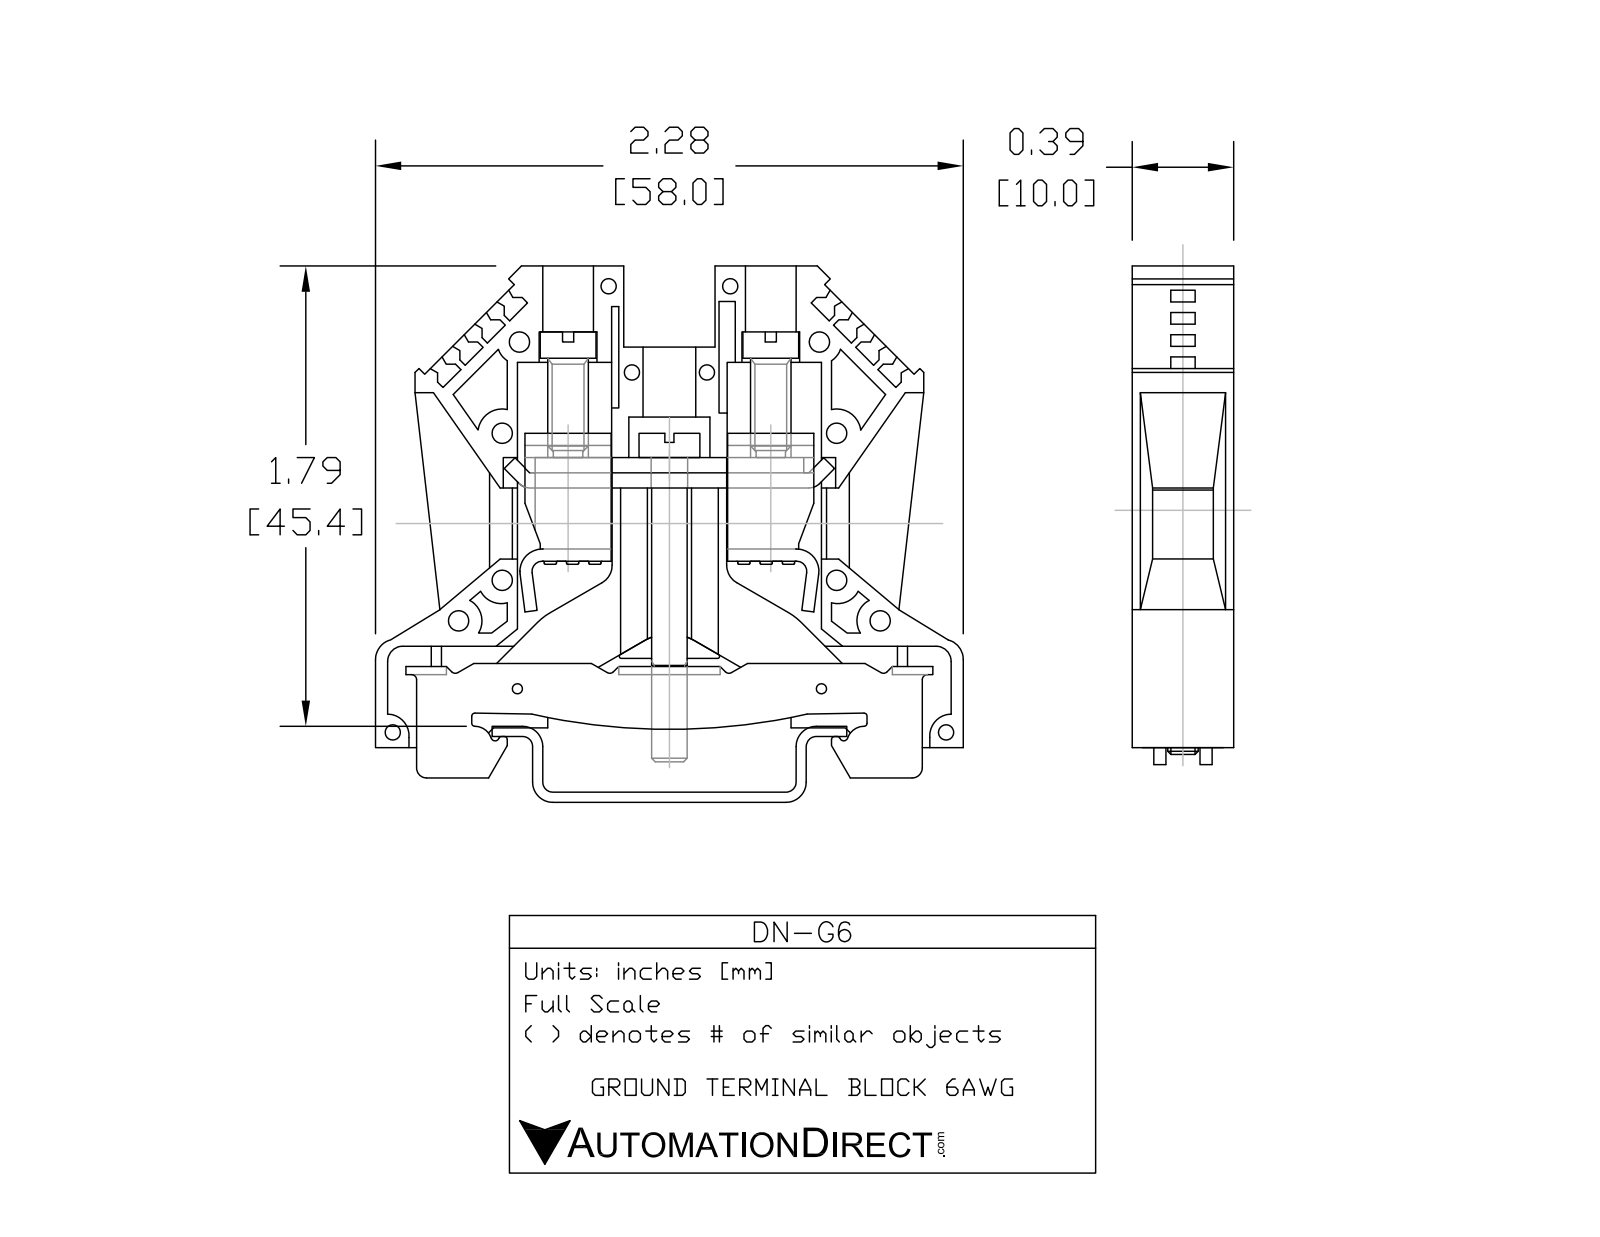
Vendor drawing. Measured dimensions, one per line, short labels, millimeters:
name: 20348; 43458_DN-G6
written by: SolidWorks 2013 (AUTOMOTIVE_DESIGN)
unit: mm
bodies: 1 solid, 477 faces (219 planar, 174 cylindrical, 84 other)
size: 58 × 49 × 10
volume: 17 767 mm³; area: 8 642 mm²
holes: 8× ⌀2.1, 8× ⌀2.3, 6× ⌀1.6, 6× ⌀1.8, 2× ⌀5, 2× ⌀5.7, 1× ⌀5.2
bosses: 8× ⌀1.7, 6× ⌀1.2
rounds: 4× R0.3, 2× R0.4, 2× R1, 2× R1.7, 2× R2.7, 1× R62
face distances: 10, 9.3, 0.7, 8.6, 0.8, 24.5, 43.5, 33.5, 4, 47.5
hole spacings: 5.8, 8.81, 9.16, 10, 10.38, 11.5, 12.9, 12.93
